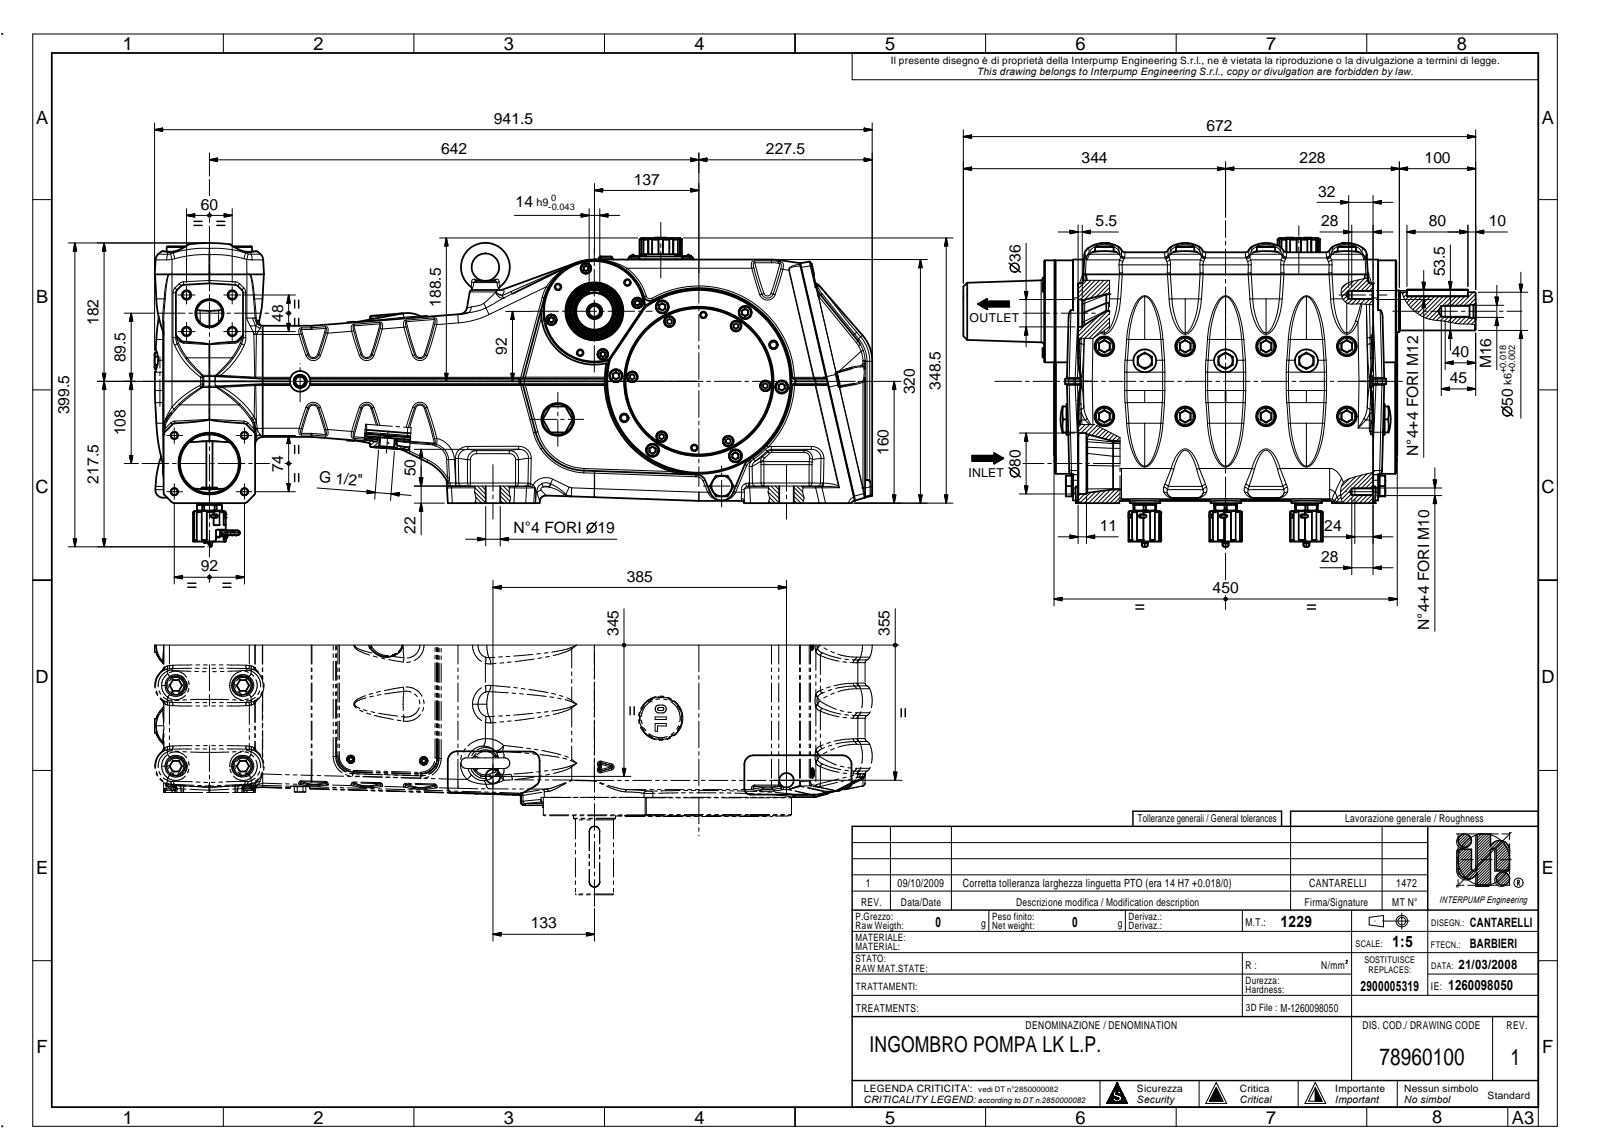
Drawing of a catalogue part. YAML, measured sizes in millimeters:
step_written_by: "THINKDESIGN (CONFIG_CONTROL_DESIGN)"
units: millimeters
bodies: {solids: 137, faces: 11259, planar: 0, cylindrical: 0, other: 11259}
overall_size: [941.49, 672, 406.21]
volume: 84950000
surface_area: 3670000
